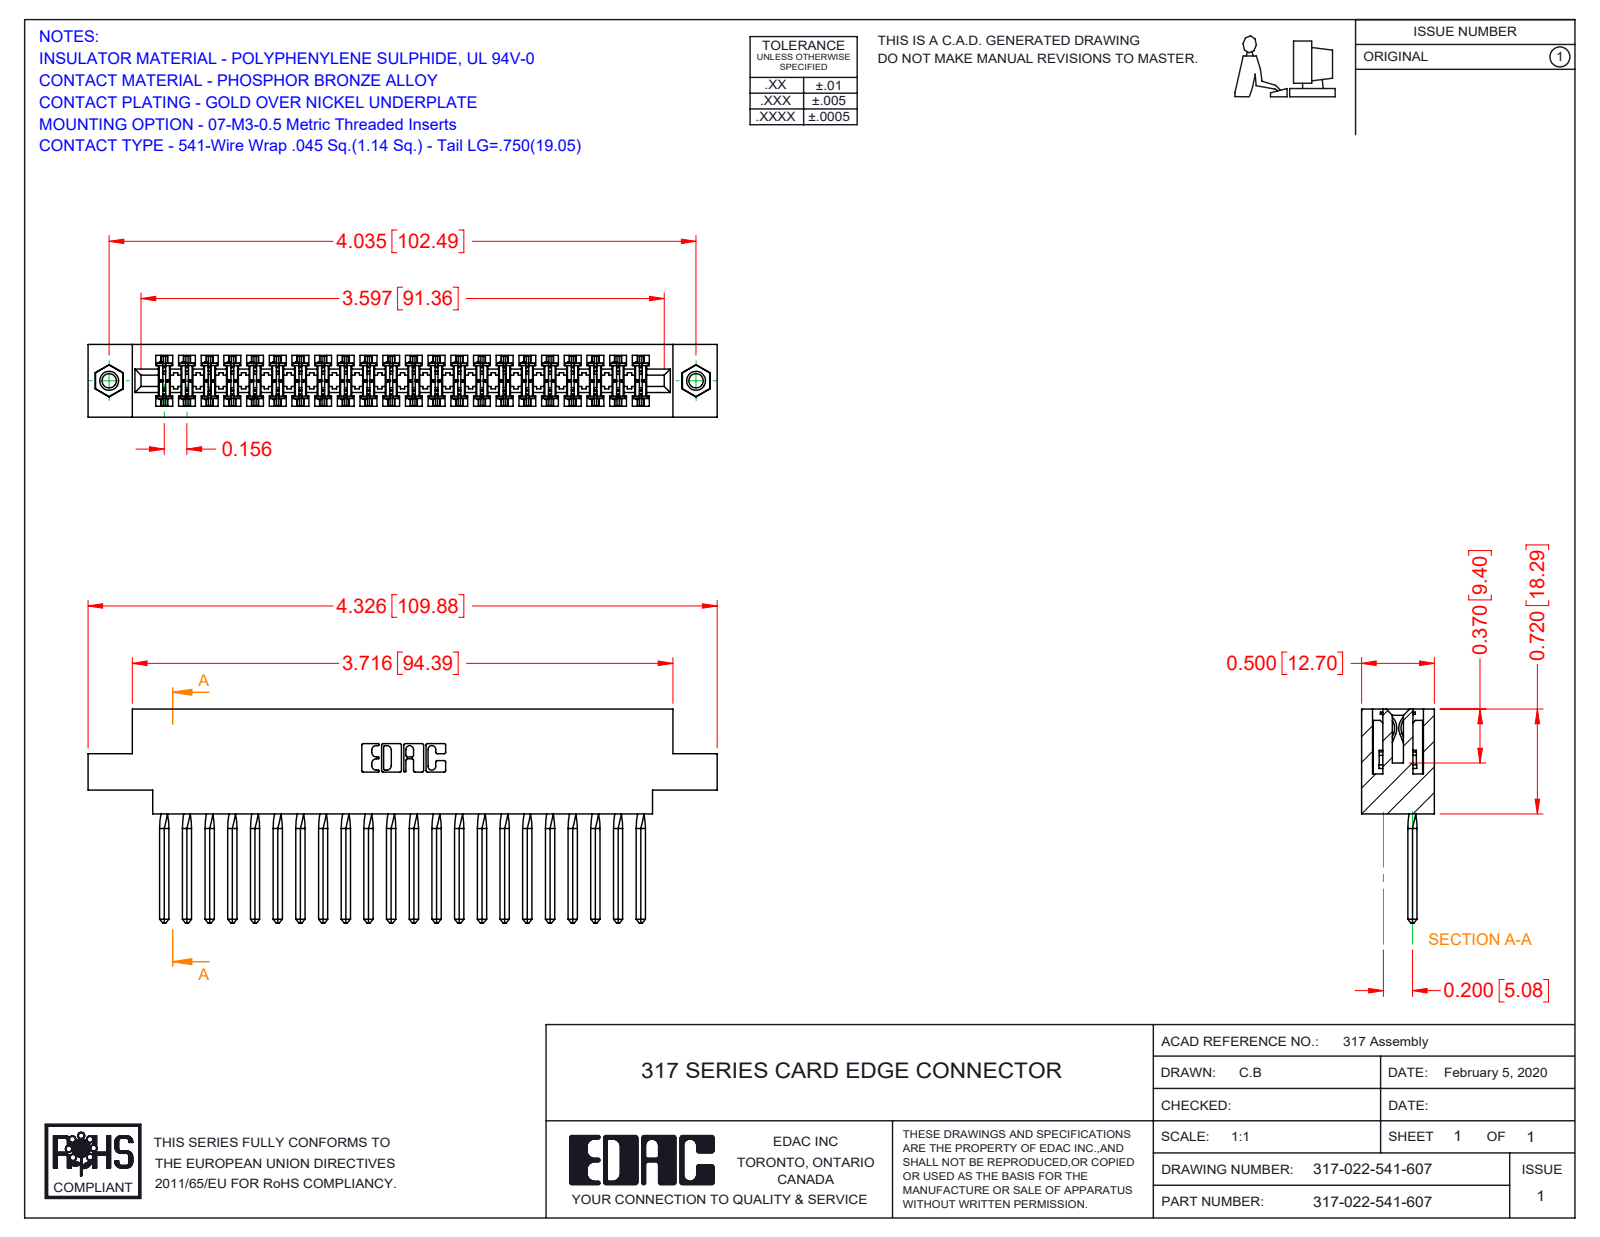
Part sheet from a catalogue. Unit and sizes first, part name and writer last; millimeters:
Units: millimetres
Overall size (bounding box): 109.9 × 37.3 × 12.7
Round holes (diameter × count): ⌀2.5 ×2, ⌀3.2 ×2, ⌀4 ×2
Round bosses / shafts (diameter × count): ⌀3.9 ×2
Partial cylindrical surfaces — rounded edges, fillets, slot ends (radius × count): R0.4 ×44, R0.3 ×22, R0.2 ×6, R0.8 ×6, R0.7 ×3, R2.4 ×2, R2.5 ×2, R2.8 ×2
Main face-to-face distances: 12.7, 1.9, 10.8, 2.8, 8.9, 5, 19.6, 5.6, 16.8, 18.3
Hole centre spacings: 102.5
Volume: 17 190 mm³ · Surface area: 23 660 mm²
Bodies: 25 solids, 3506 faces (2818 planar, 584 cylindrical, 104 other)
Part name (STEP PRODUCT): 345-250-001_345-250-005-103; 317 Part_.156 Dia - TI; 317-290-002_541; 317-022-541-607
STEP written by: SolidWorks 2016 (CONFIG_CONTROL_DESIGN)
